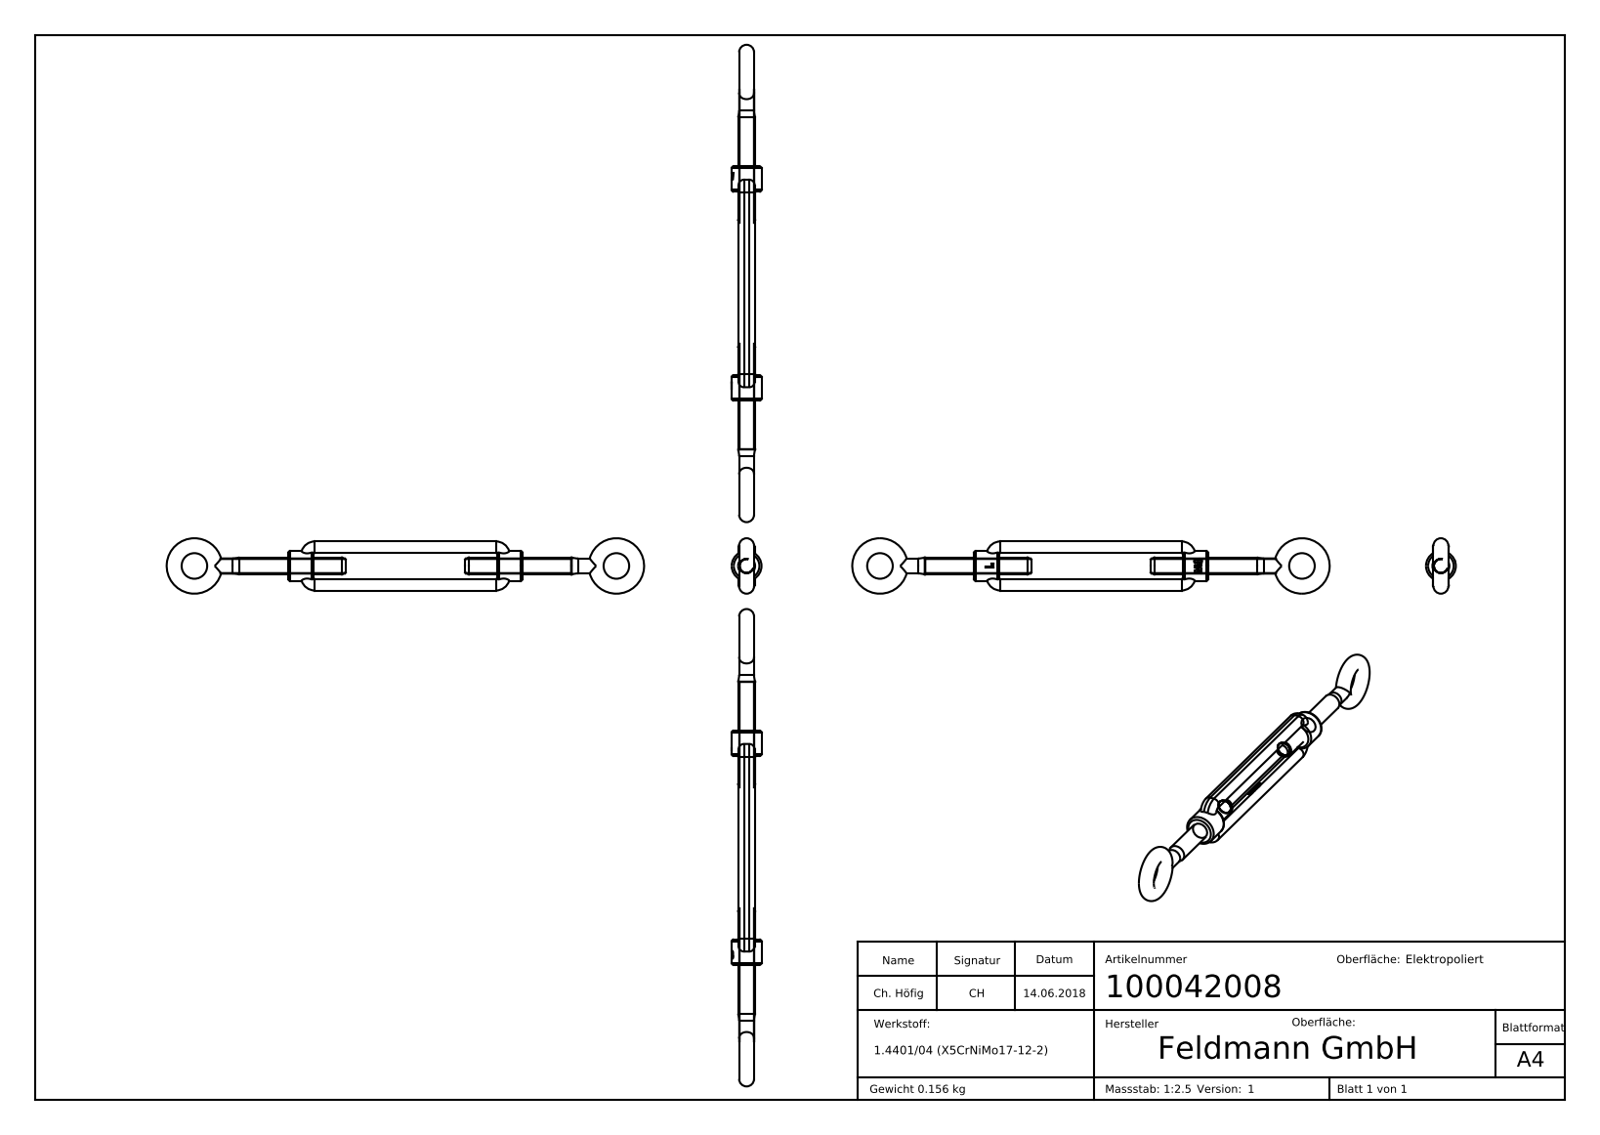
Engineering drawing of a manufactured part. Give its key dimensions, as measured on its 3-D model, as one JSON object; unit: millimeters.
{"part_name": "10004200X Teil2_100042008 Teil2; 10004200X Teil1_100042008 Teil1; 100042008; 10004200X Teil3_100042008 Teil3", "step_written_by": "SolidWorks 2015 (CONFIG_CONTROL_DESIGN)", "units": "millimeters", "bodies": {"solids": 3, "faces": 343, "planar": 128, "cylindrical": 33, "other": 182}, "overall_size": [224, 26, 14], "volume_mm3": 19526, "surface_area_mm2": 11311, "round_holes": [[6.8, 1]], "round_bosses_or_shafts": [[14, 1], [8, 1], [7, 1]], "partial_cylinders_radius": [[1, 4], [2.75, 4], [6.5, 4], [6.98, 1]], "face_to_face_distances": [5.5, 17.5, 12, 23, 98, 110, 86, 27, 83, 15]}
